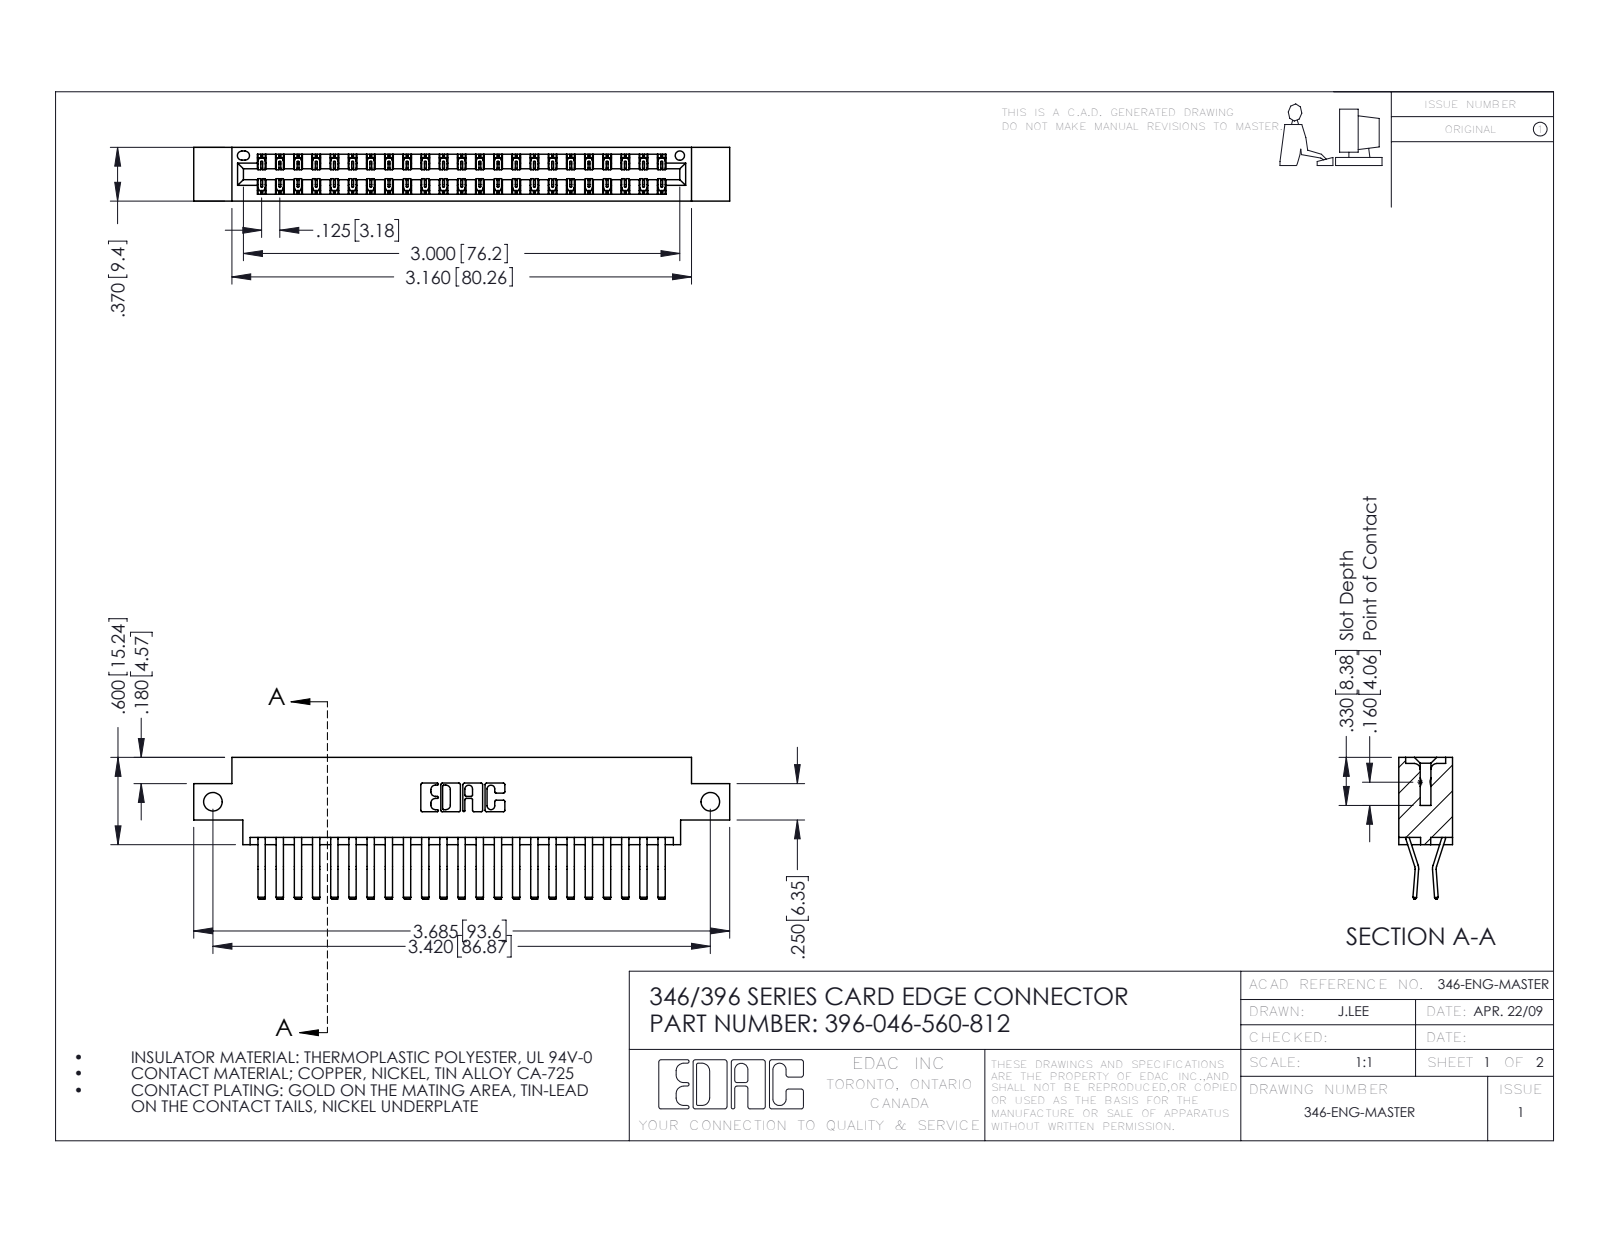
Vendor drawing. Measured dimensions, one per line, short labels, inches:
name: 396-046-560-812; 346 Part_0.170 Offset - Side Mount; 345-292-001_560 Tail
written by: SolidWorks 2016 (CONFIG_CONTROL_DESIGN)
unit: in
bodies: 47 solids, 2610 faces (1690 planar, 920 cylindrical, 0 other)
size: 3.685 × 0.975 × 0.37
volume: 0.552 in³; area: 20.11 in²
holes: 2× ⌀0.128, 1× ⌀0.064
rounds: 69× R0.006, 22× R0.01, 6× R0.007, 6× R0.031, 3× R0.026, 2× R0.01, 2× R0.014, 2× R0.022
face distances: 0.048, 0.322, 0.37, 0.25, 0.025, 0.072, 0.298, 0.275, 0.148, 0.222
hole spacings: 3.42
